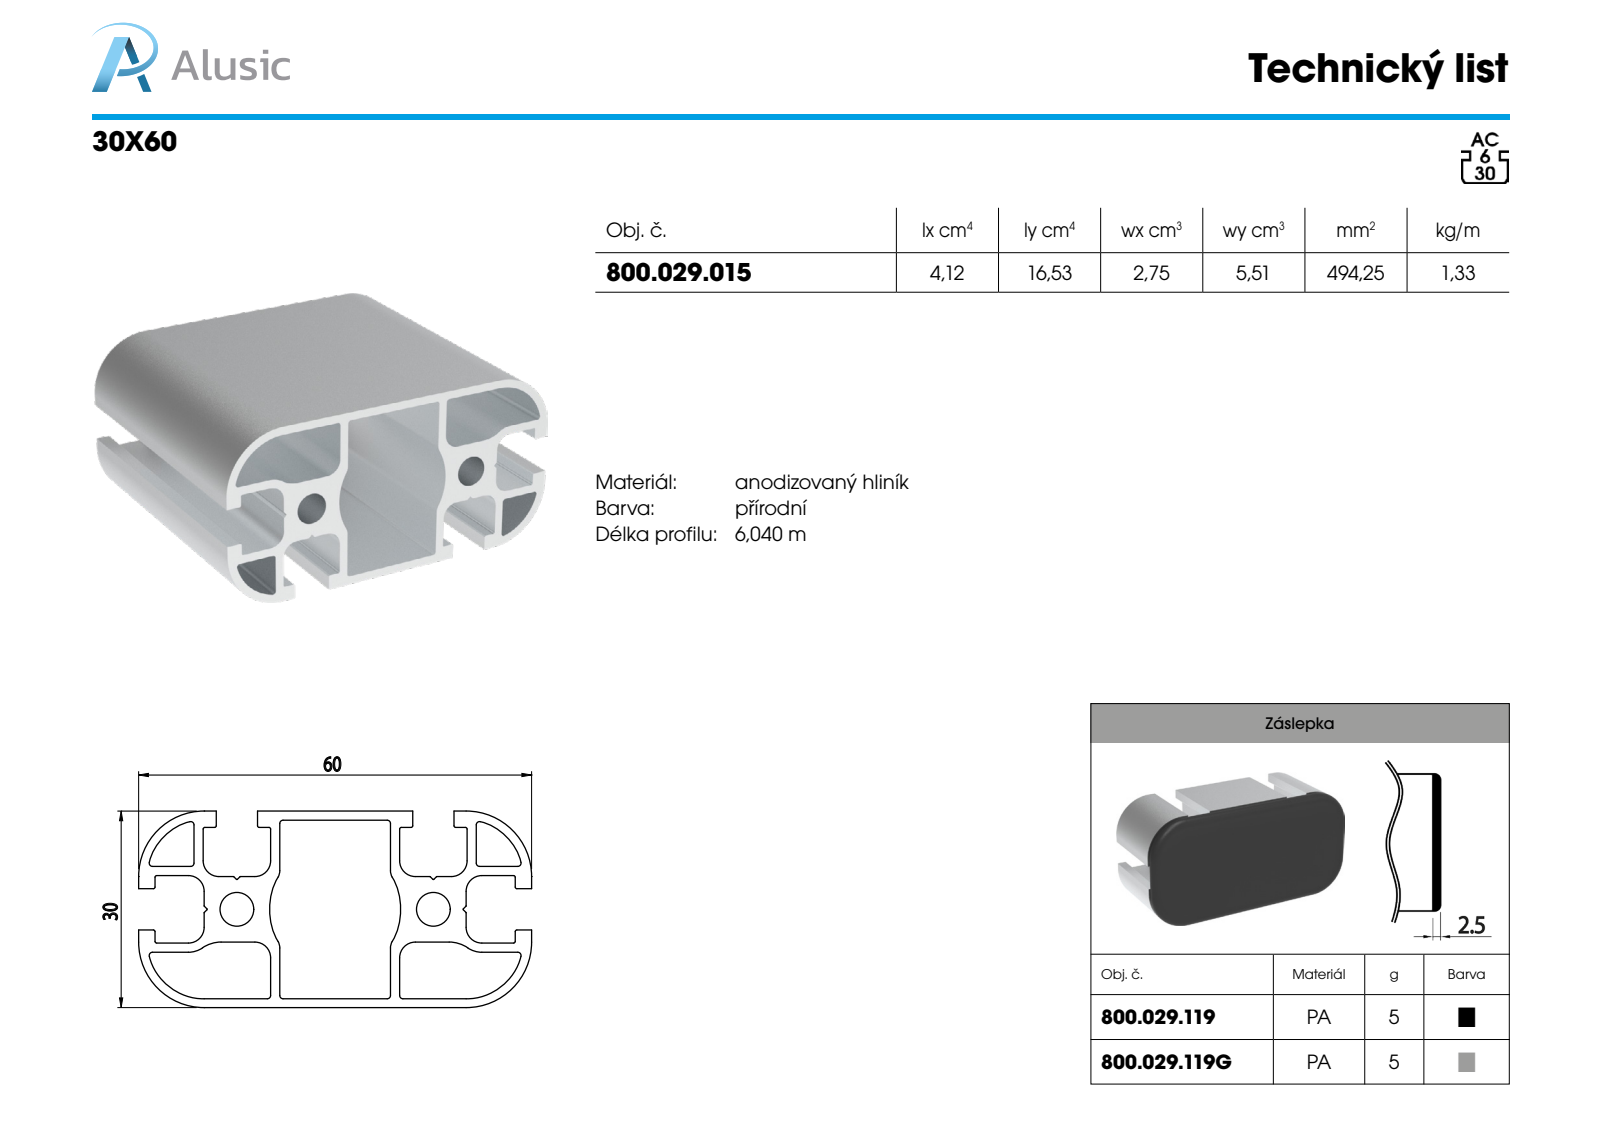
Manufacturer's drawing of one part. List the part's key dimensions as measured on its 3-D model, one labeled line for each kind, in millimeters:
Part name (STEP PRODUCT): 800.029.015
STEP written by: SolidWorks 2012 (CONFIG_CONTROL_DESIGN)
Units: millimetres
Bodies: 1 solid, 144 faces (68 planar, 76 cylindrical, 0 other)
Overall size (bounding box): 100 × 60 × 30
Volume: 49 425 mm³ · Surface area: 54 044 mm²
Round holes (diameter × count): ⌀5.15 ×2
Partial cylindrical surfaces — rounded edges, fillets, slot ends (radius × count): R0.25 ×16, R0.5 ×14, R0.1 ×12, R2.4 ×10, R10 ×5, R2 ×4, R8.65 ×4, R3.8 ×2
Main face-to-face distances: 1.4, 30, 11.7, 8.45, 20.15, 10, 1.35, 21.55, 1.55, 11.55
Hole centre spacings: 30
